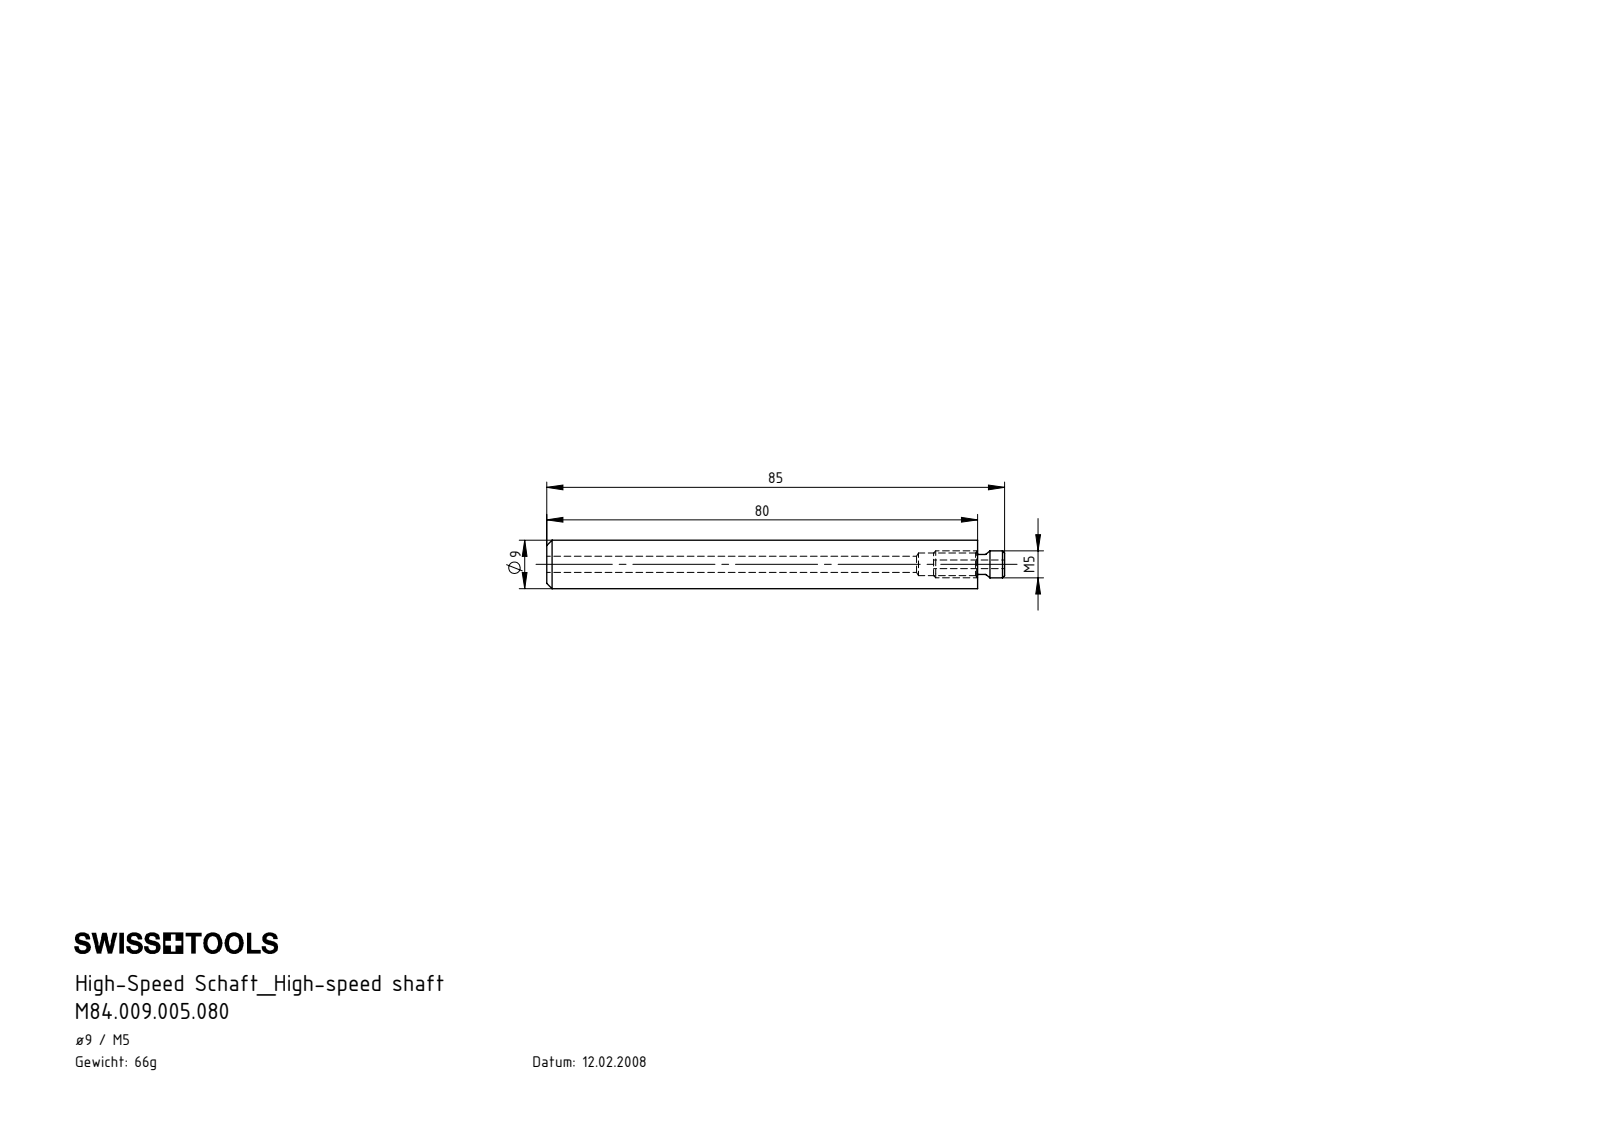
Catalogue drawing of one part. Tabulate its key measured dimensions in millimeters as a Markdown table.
| quantity | value |
| --- | --- |
| part name | HM1-U09.001.080_A; HM1-BG1.005.013_A; U09.HS5.K01.080 |
| STEP written by | SolidWorks 2017 (AUTOMOTIVE_DESIGN) |
| units | millimeters |
| bodies | 2 solids, 20 faces (5 planar, 7 cylindrical, 8 other) |
| overall size | 85 × 9 × 9 |
| volume | 4 646 mm³ |
| surface area | 3 450 mm² |
| round holes (diameter × count) | 1.6 × 1, 3 × 1, 4.2 × 1 |
| round bosses / shafts (diameter × count) | 9 × 1, 5 × 1, 3.7 × 1 |
| main face-to-face distances | 80, 71.8, 8.2, 85, 13.2, 5, 79.8, 8, 5.2 |
